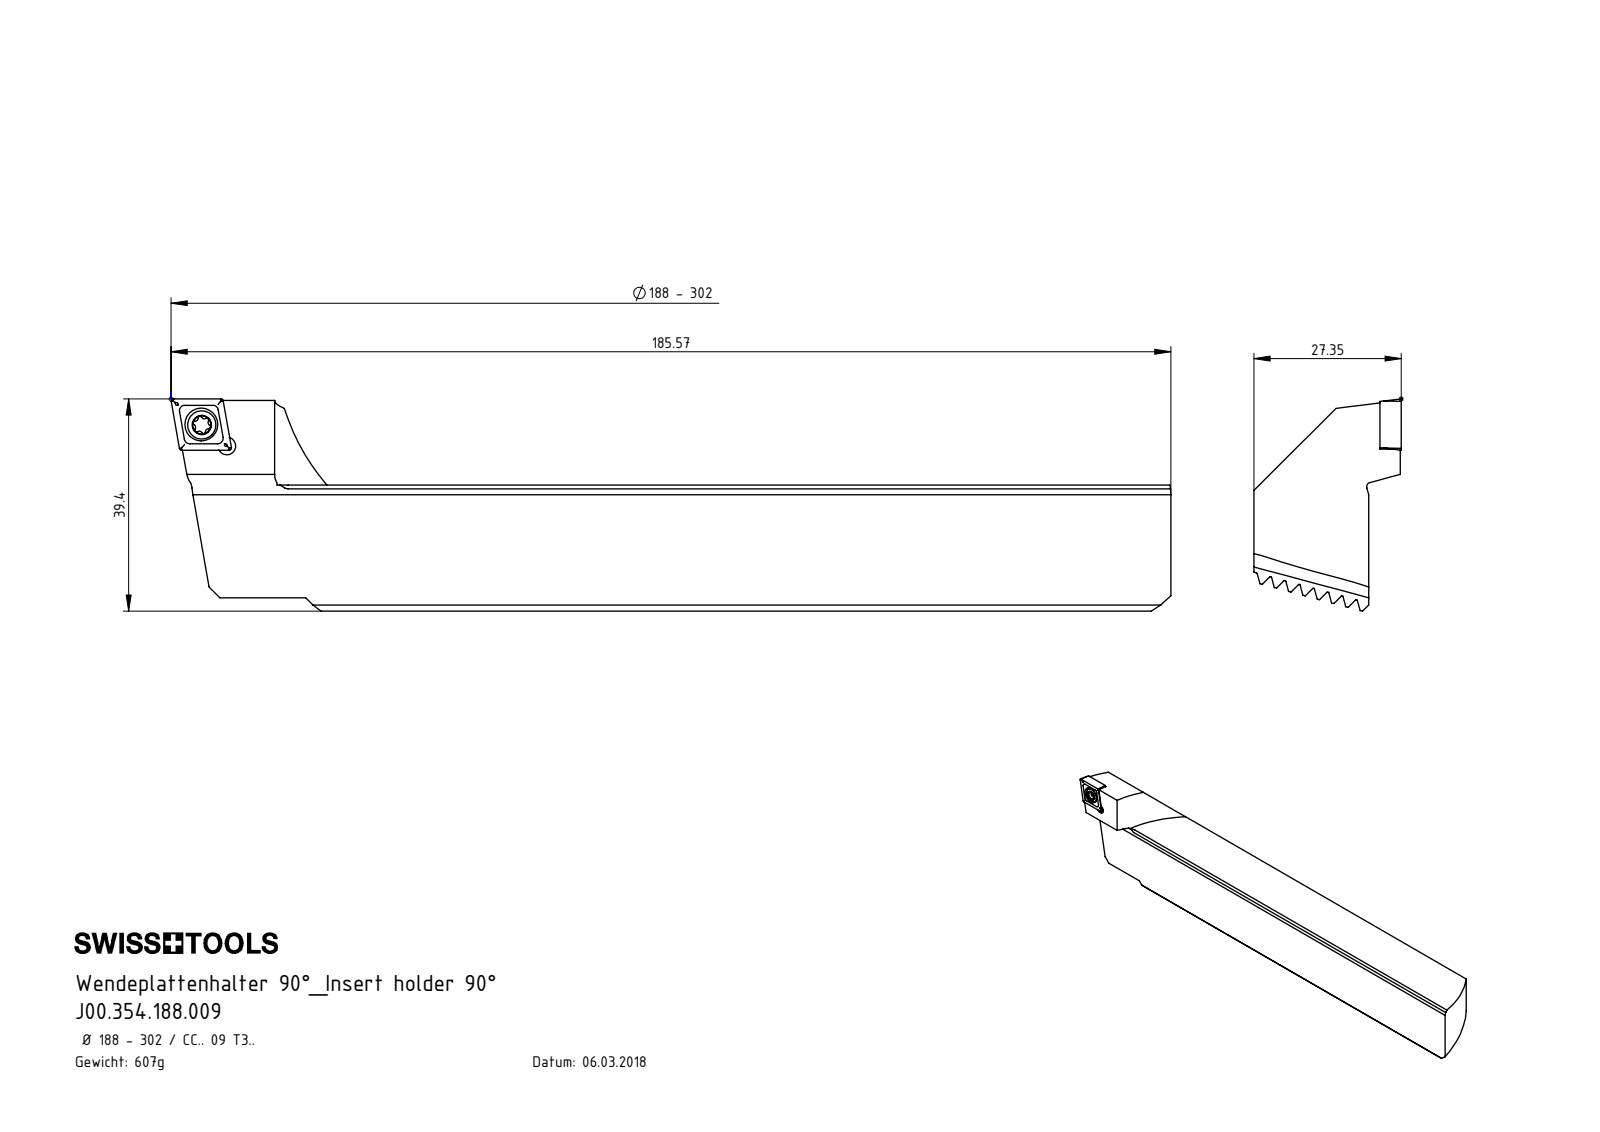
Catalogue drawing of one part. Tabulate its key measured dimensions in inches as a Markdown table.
| quantity | value |
| --- | --- |
| part name | J00.354.188.009; CCMT09T304; WCB-ER2.001.009_A; F00-WCB.188.001_C |
| STEP written by | SolidWorks 2017 (CONFIG_CONTROL_DESIGN) |
| units | inches |
| bodies | 3 solids, 694 faces (422 planar, 39 cylindrical, 233 other) |
| overall size | 7.306 × 1.551 × 1.077 |
| volume | 4.719 in³ |
| surface area | 29.34 in² |
| round holes (diameter × count) | 0.13 × 2, 0.173 × 1, 0.24 × 1 |
| round bosses / shafts (diameter × count) | 0.207 × 1, 0.157 × 1 |
| partial cylindrical surfaces (radius × count) | 0.008 × 8, 0.013 × 6, 0.023 × 6, 1.575 × 3, 0.031 × 1 |
| main face-to-face distances | 0.094, 0.839, 0.187, 0.281, 0.375, 0.188, 0.281, 0.375, 0.469, 0.563 |
| hole center spacings | 0.239, 0.244 |
